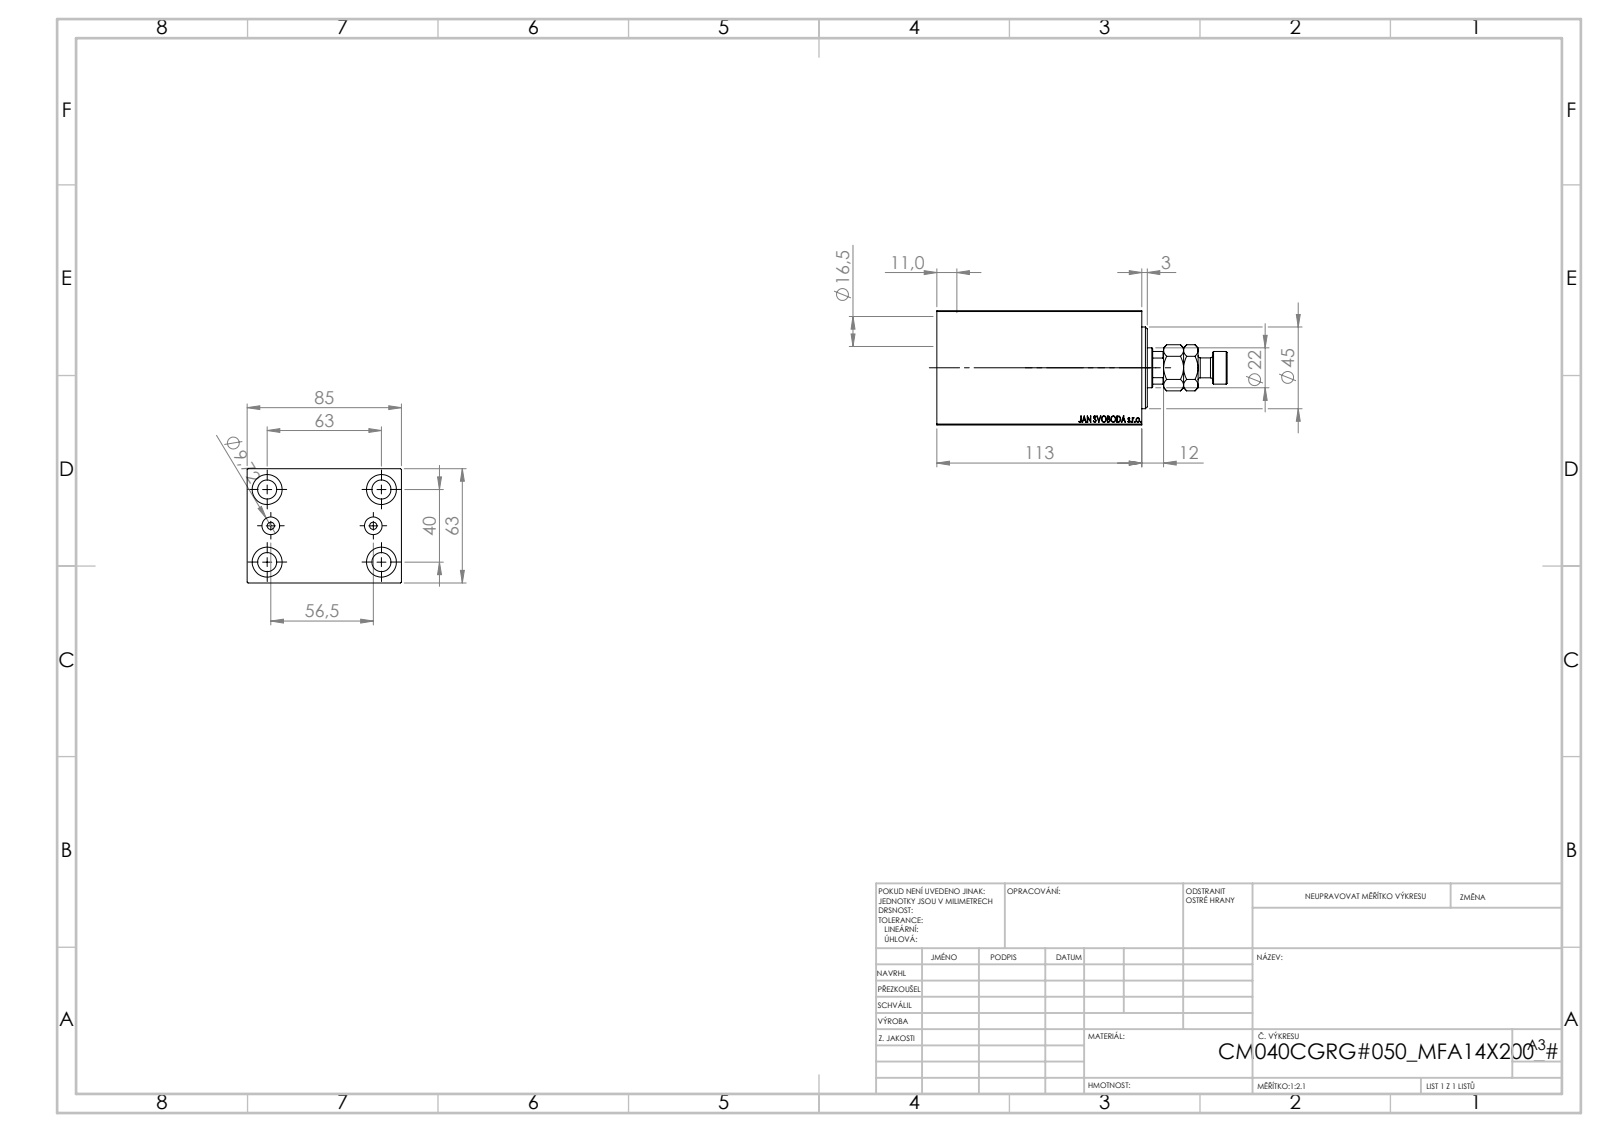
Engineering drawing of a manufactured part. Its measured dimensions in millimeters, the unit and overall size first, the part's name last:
Units: millimetres
Overall size (bounding box): 160 × 85 × 63
Round holes (diameter × count): ⌀10.5 ×4, ⌀16.5 ×4, ⌀4 ×2, ⌀9.72 ×2, ⌀12.5 ×1, ⌀22 ×1, ⌀25.5 ×1, ⌀40 ×1, ⌀42 ×1, ⌀45 ×1
Round bosses / shafts (diameter × count): ⌀18 ×1, ⌀11 ×1
Partial cylindrical surfaces — rounded edges, fillets, slot ends (radius × count): R10.5 ×1
Main face-to-face distances: 63, 85, 113, 12, 101, 28.6, 72.4, 84.4, 11, 102
Hole centre spacings: 20.26, 37.31, 63.01, 28.25, 40, 63, 74.63, 56.5
Volume: 522 510 mm³ · Surface area: 100 269 mm²
Bodies: 4 solids, 910 faces (424 planar, 60 cylindrical, 426 other)
Part name (STEP PRODUCT): MFA; V450CM_C_Body; V450CM_C_VCP; V450CM_VC_B
STEP written by: SolidWorks 2019 (CONFIG_CONTROL_DESIGN)
